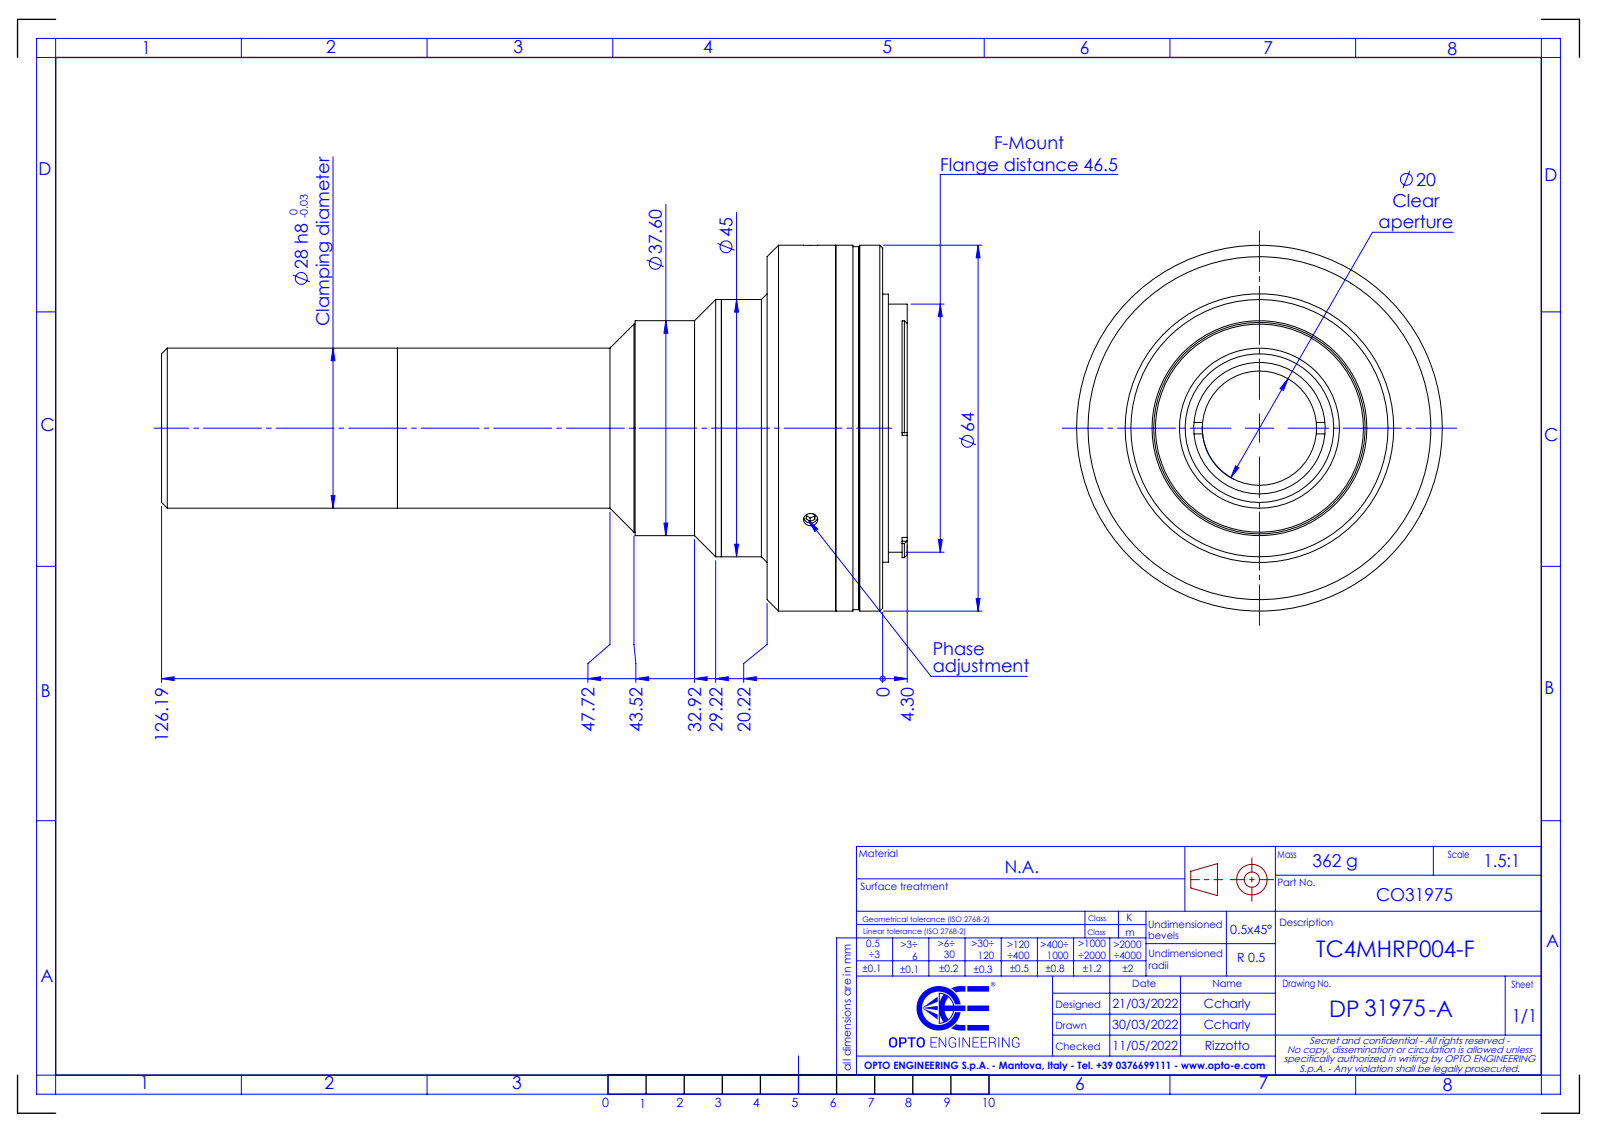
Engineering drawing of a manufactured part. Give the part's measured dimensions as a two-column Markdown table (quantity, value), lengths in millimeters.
| quantity | value |
| --- | --- |
| part name | DP31975-A_TC4MHRP004-F |
| STEP written by | SolidWorks 2021 (CONFIG_CONTROL_DESIGN) |
| units | millimeters |
| bodies | 0 solids, 127 faces (46 planar, 55 cylindrical, 26 other) |
| overall size | 130.49 × 64 × 64 |
| round holes (diameter × count) | 2.5 × 3, 20 × 1, 23 × 1, 34.8 × 1, 36.4 × 1, 42 × 1 |
| round bosses / shafts (diameter × count) | 64 × 1, 63.5 × 1, 46.9 × 1, 45 × 1, 43.4 × 1, 37.6 × 1, 28 × 1 |
| partial cylindrical surfaces (radius × count) | 0.5 × 6, 1.15 × 2, 22.65 × 1 |
| main face-to-face distances | 18.72, 10.52, 8.2, 1.5, 13.52, 3, 5.2, 12.02, 15.02, 20.22 |
